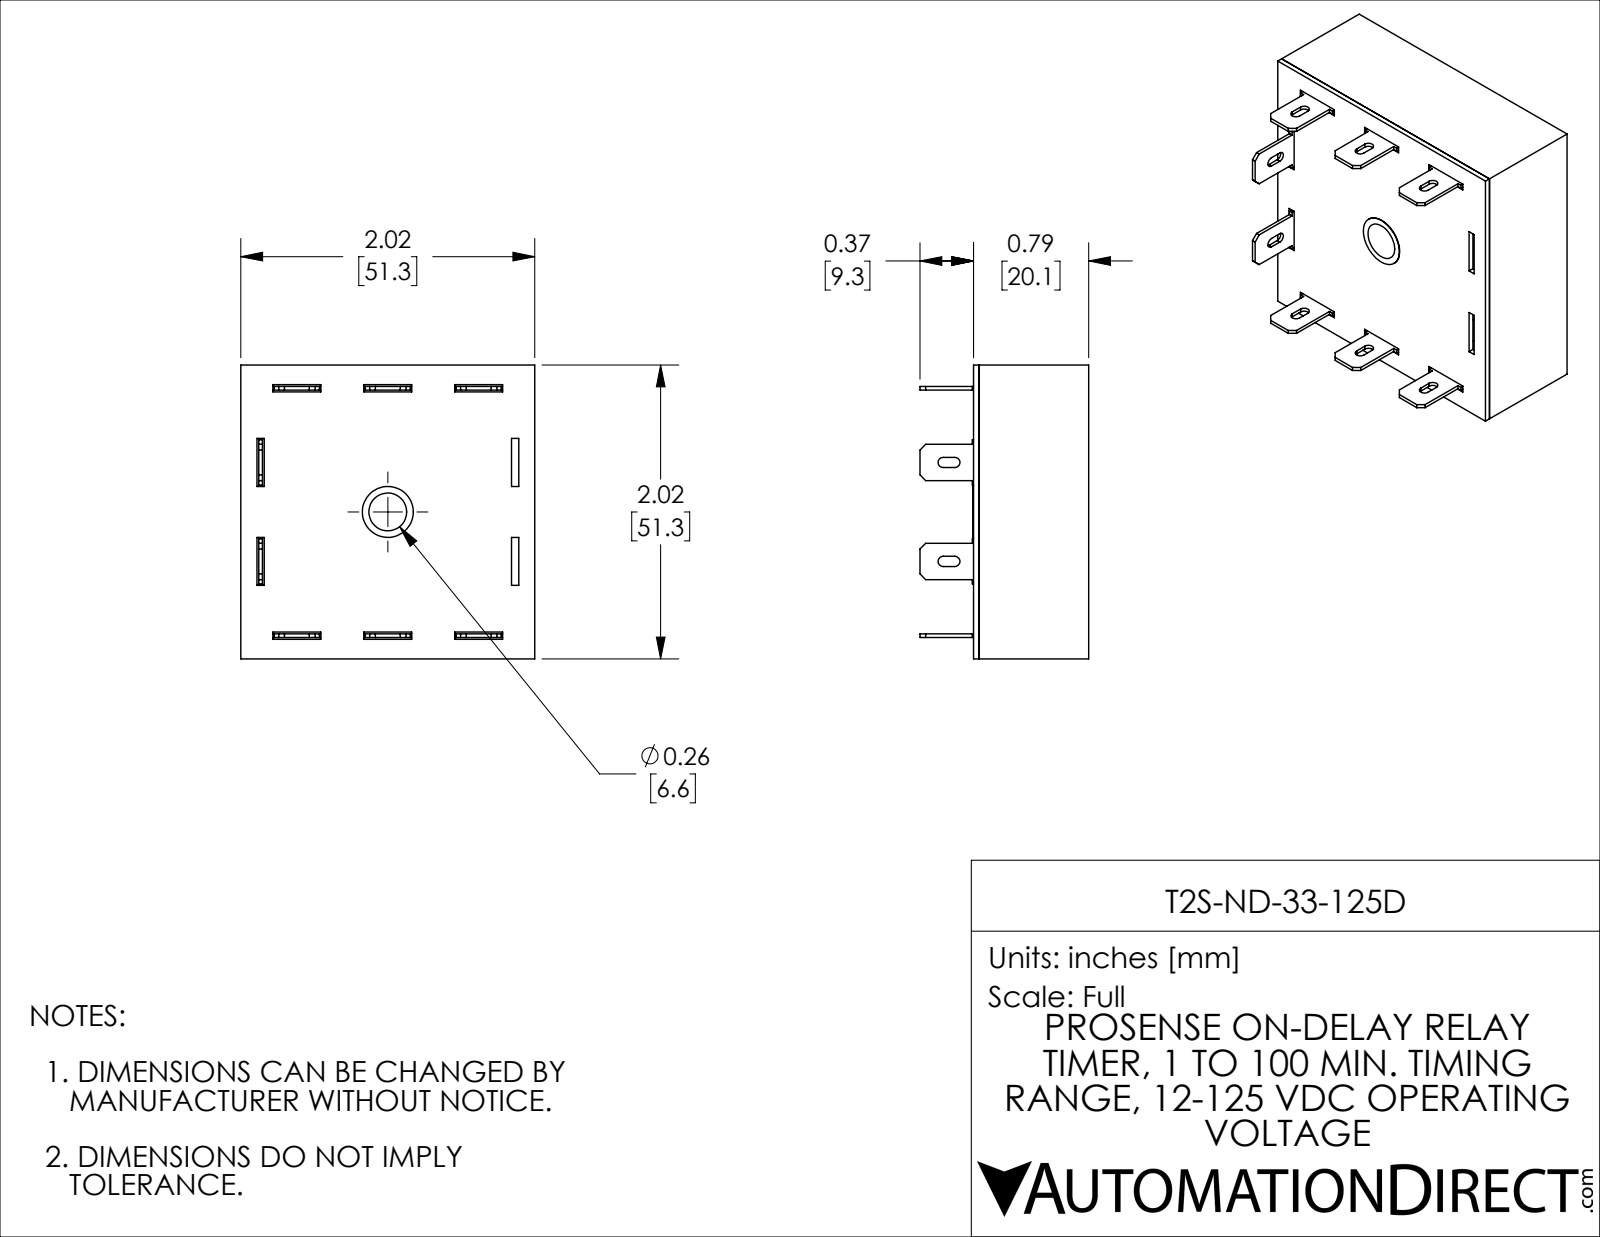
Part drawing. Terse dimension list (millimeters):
name: T2S-ND-33-125D
written by: SolidWorks 2021 (CONFIG_CONTROL_DESIGN)
unit: mm
bodies: 10 solids, 256 faces (234 planar, 20 cylindrical, 2 other)
size: 51.31 × 51.31 × 29.46
volume: 11 042 mm³; area: 22 819 mm²
holes: 1× ⌀8.89
rounds: 10× R0.89
face distances: 1.14, 50.16, 19.15, 20.12, 0.97, 18.01, 18.98, 51.3, 49.02, 3.74
